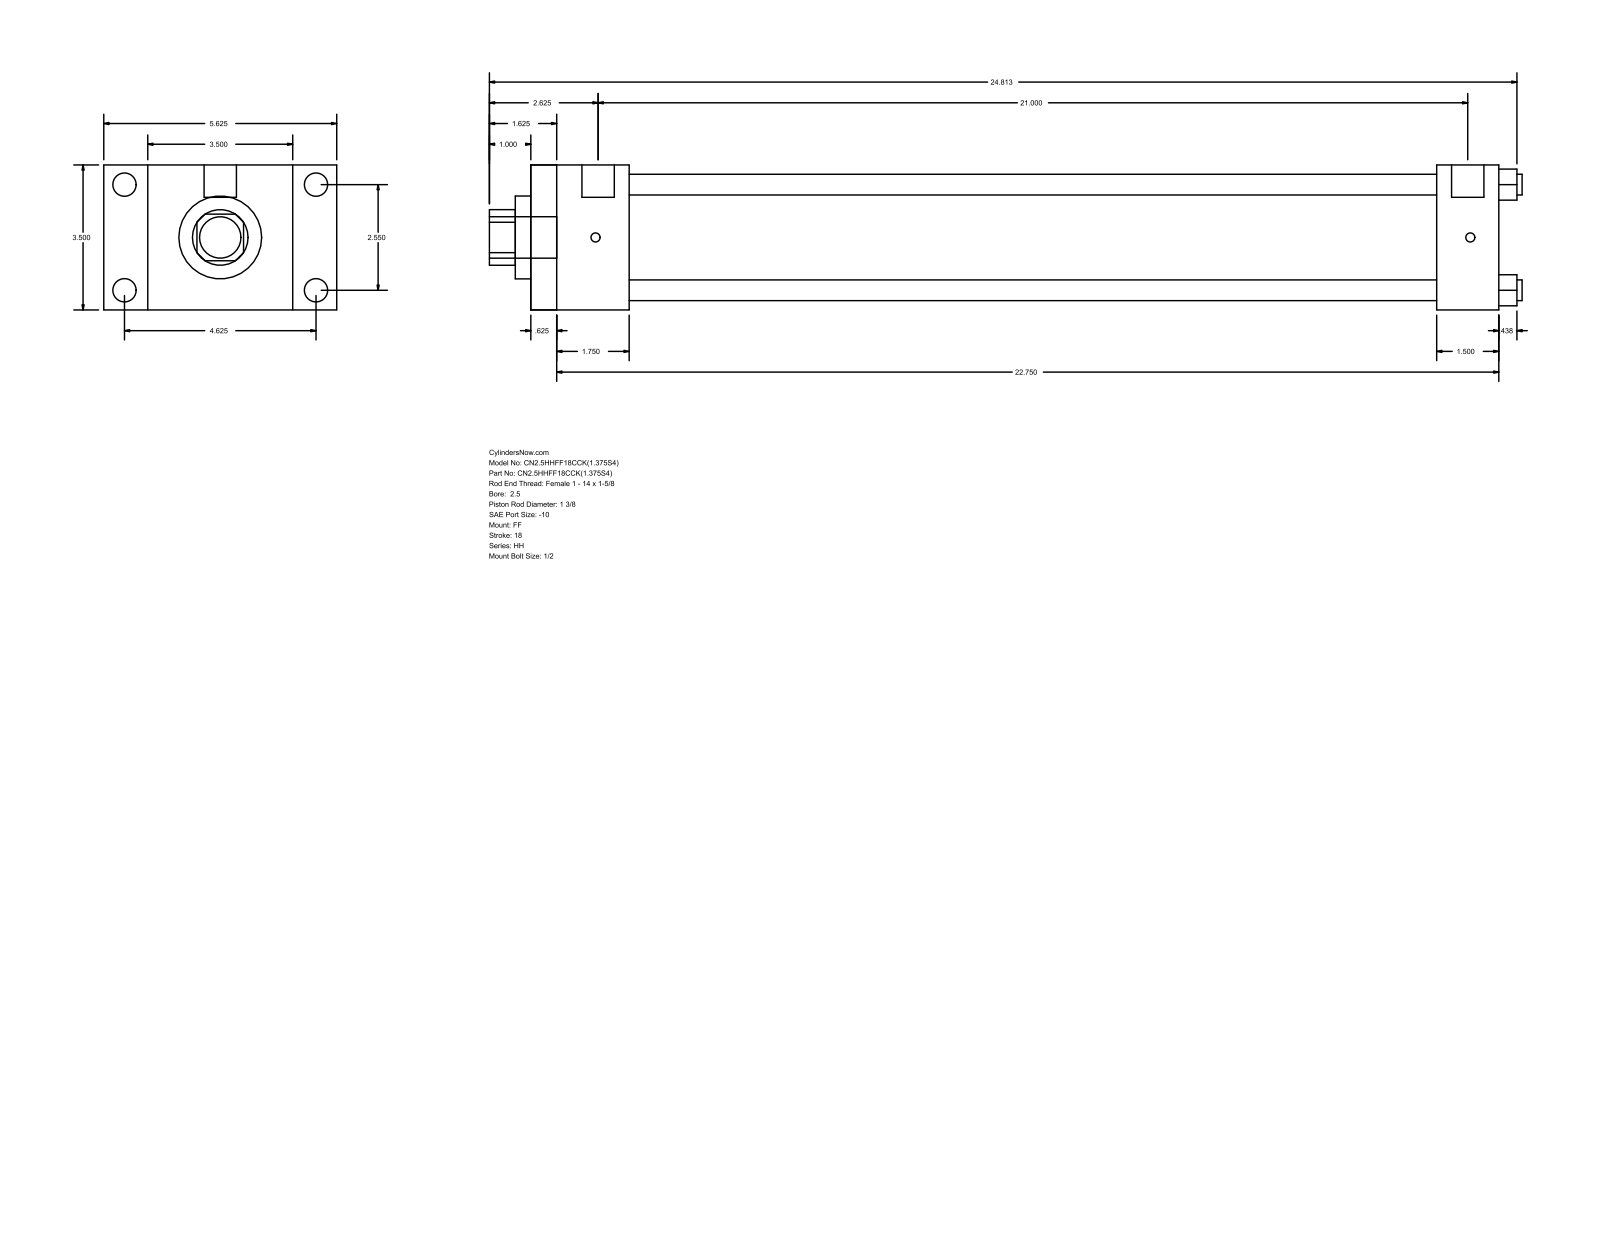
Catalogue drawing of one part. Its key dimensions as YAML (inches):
part_name: "HH_FF__0250_1.375"
step_written_by: "GSSL Pune (CONFIG_CONTROL_DESIGN)"
units: inches
bodies: {solids: 0, faces: 92, planar: 64, cylindrical: 28, other: 0}
overall_size: [24.937, 5.625, 3.5]
round_holes:
  - {diameter: 0.5, count: 4}
  - {diameter: 1.375, count: 1}
  - {diameter: 2, count: 1}
  - {diameter: 2.875, count: 1}
round_bosses_or_shafts:
  - {diameter: 0.563, count: 4}
  - {diameter: 0.219, count: 4}
  - {diameter: 0.781, count: 2}
  - {diameter: 1, count: 1}
partial_cylinders:
  - {radius: 0.672, count: 1}
face_to_face_distances: [3.5, 23.375, 0.625, 22.75, 2.375, 1.75, 21, 21.875, 21.25, 19.5]
hole_center_spacings: [1.803, 2.55, 3.606]
